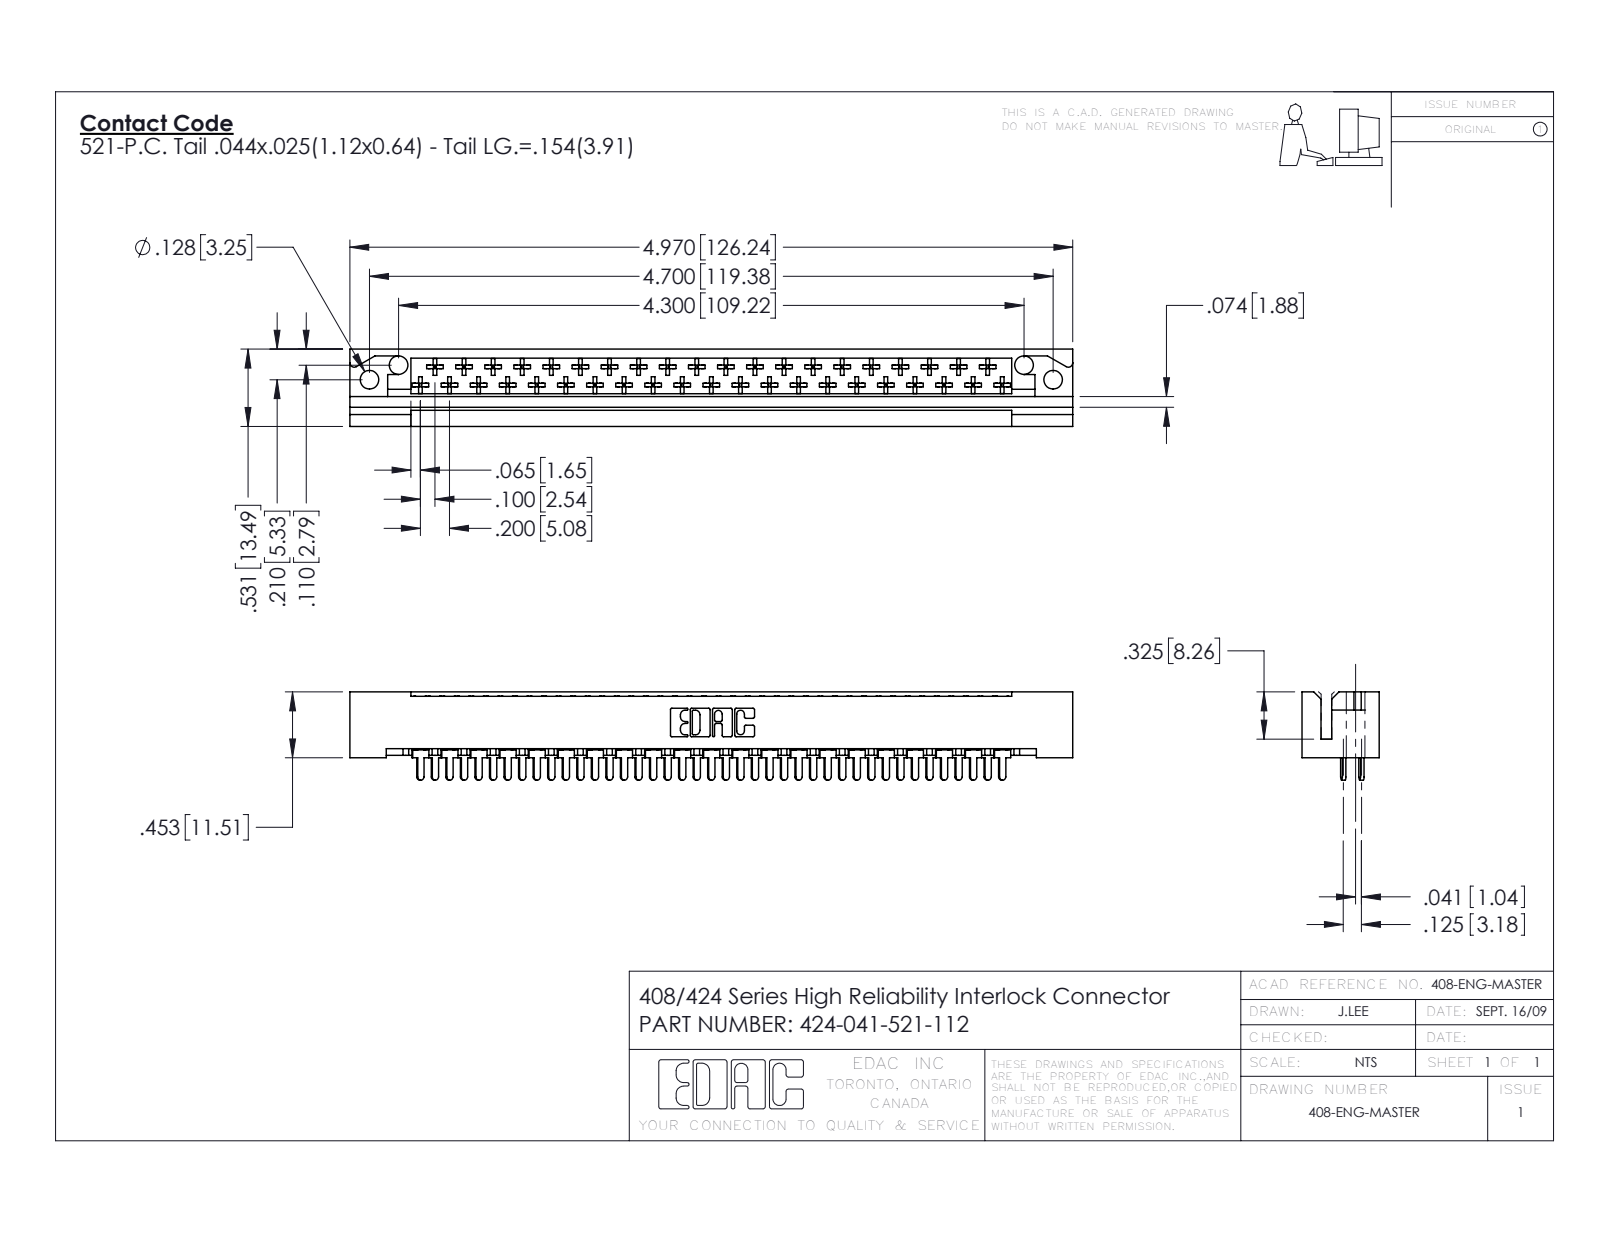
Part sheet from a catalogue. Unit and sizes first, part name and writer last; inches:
Units: inches
Overall size (bounding box): 4.97 × 0.607 × 0.531
Round holes (diameter × count): ⌀0.128 ×4
Partial cylindrical surfaces — rounded edges, fillets, slot ends (radius × count): R0.01 ×246, R0.02 ×43, R0.022 ×41, R0.01 ×22, R0.007 ×6, R0.031 ×6, R0.026 ×3, R0.03 ×2
Main face-to-face distances: 0.025, 0.531, 0.125, 0.4, 0.1, 0.272, 0.235, 0.259, 0.025, 0.296
Hole centre spacings: 0.224, 4.501, 4.3, 4.7
Volume: 0.844 in³ · Surface area: 26.67 in²
Bodies: 42 solids, 2400 faces (1811 planar, 425 cylindrical, 164 other)
Part name (STEP PRODUCT): 408-290-001_408-290-121; 424-041-521-112; 424 Part_041
STEP written by: SolidWorks 2016 (CONFIG_CONTROL_DESIGN)
